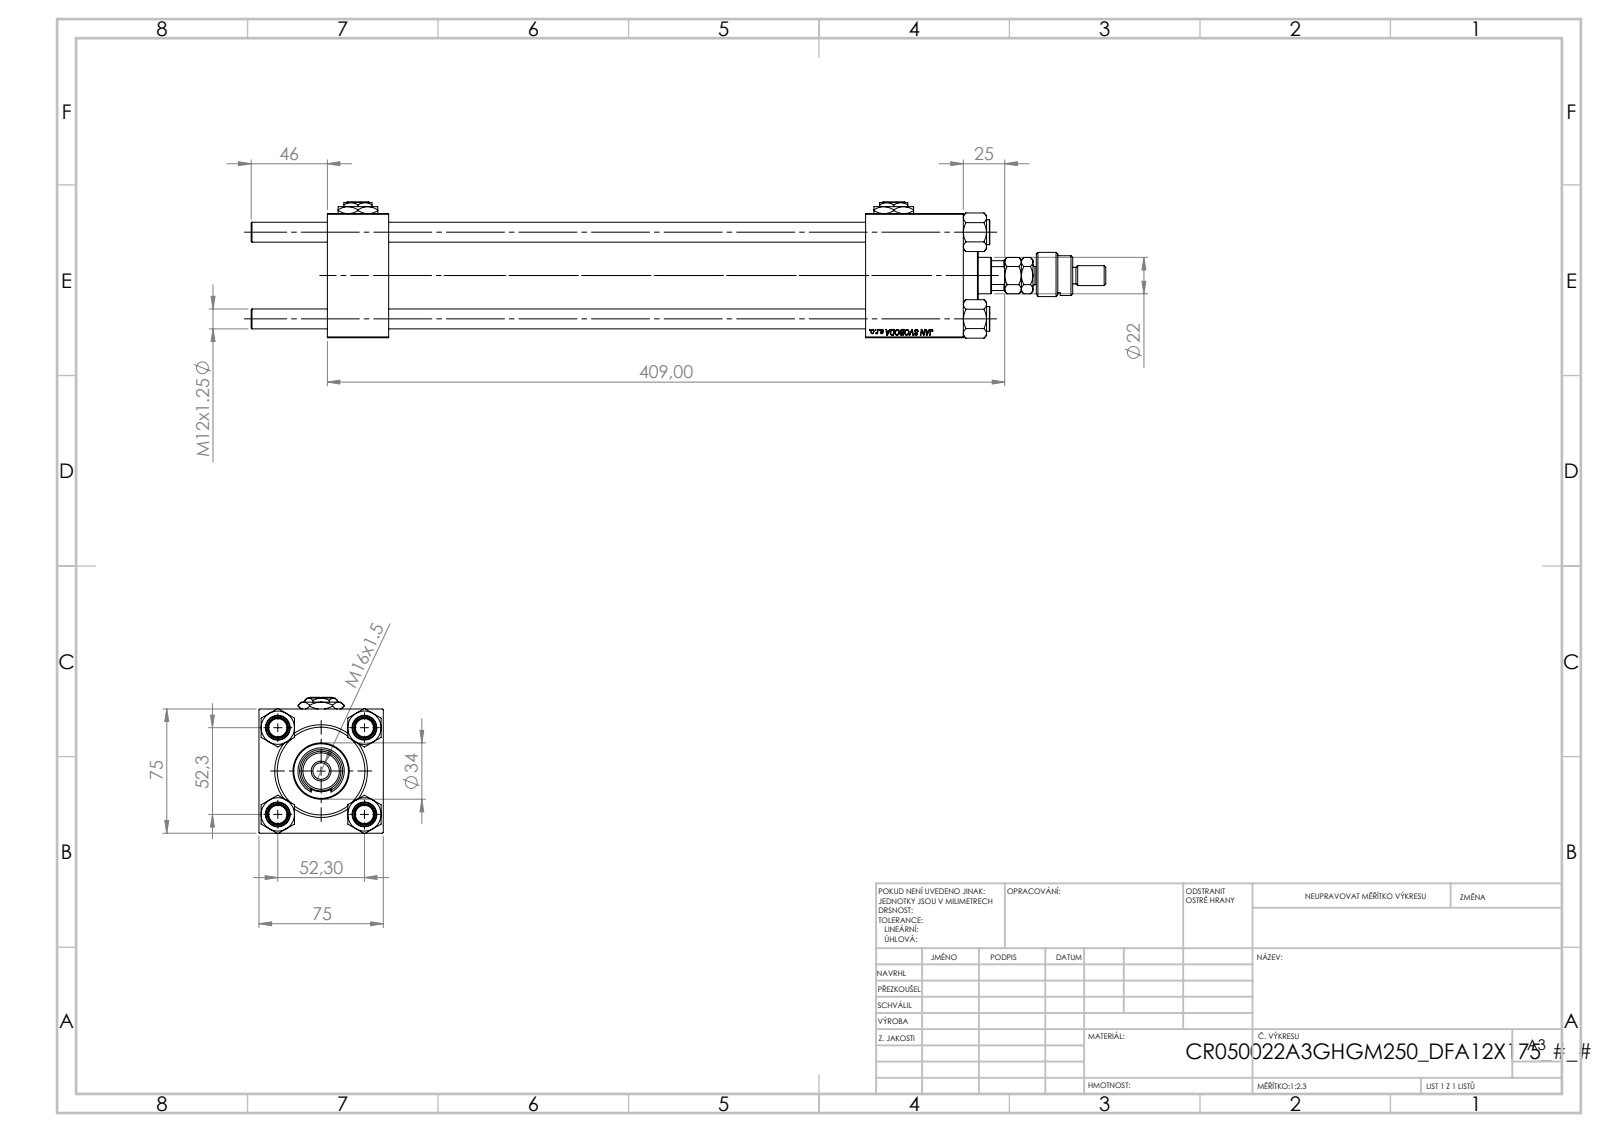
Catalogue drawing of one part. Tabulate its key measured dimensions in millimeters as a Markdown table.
| quantity | value |
| --- | --- |
| part name | MFA; V215_VC_A; V215CR_BODY_A; NUT_M5 (+4 more) |
| STEP written by | SolidWorks 2019 (CONFIG_CONTROL_DESIGN) |
| units | millimeters |
| bodies | 15 solids, 1318 faces (595 planar, 101 cylindrical, 622 other) |
| overall size | 516 × 82.27 × 75 |
| volume | 1 009 000 mm³ |
| surface area | 302 513 mm² |
| round holes (diameter × count) | 12 × 4, 7 × 2, 20.96 × 2, 30 × 2, 10.5 × 1, 22 × 1, 25 × 1, 41 × 1, 50 × 1, 53 × 1 |
| round bosses / shafts (diameter × count) | 15 × 4, 56 × 1, 34 × 1, 28 × 1, 24 × 1, 18 × 1, 12 × 1, 11 × 1 |
| partial cylindrical surfaces (radius × count) | 9.75 × 1, 10.5 × 1 |
| main face-to-face distances | 75, 37, 384, 347, 325, 288, 59, 355.3, 318.3, 30.3 |
| hole center spacings | 36.98, 52.3, 73.96, 323.5 |
